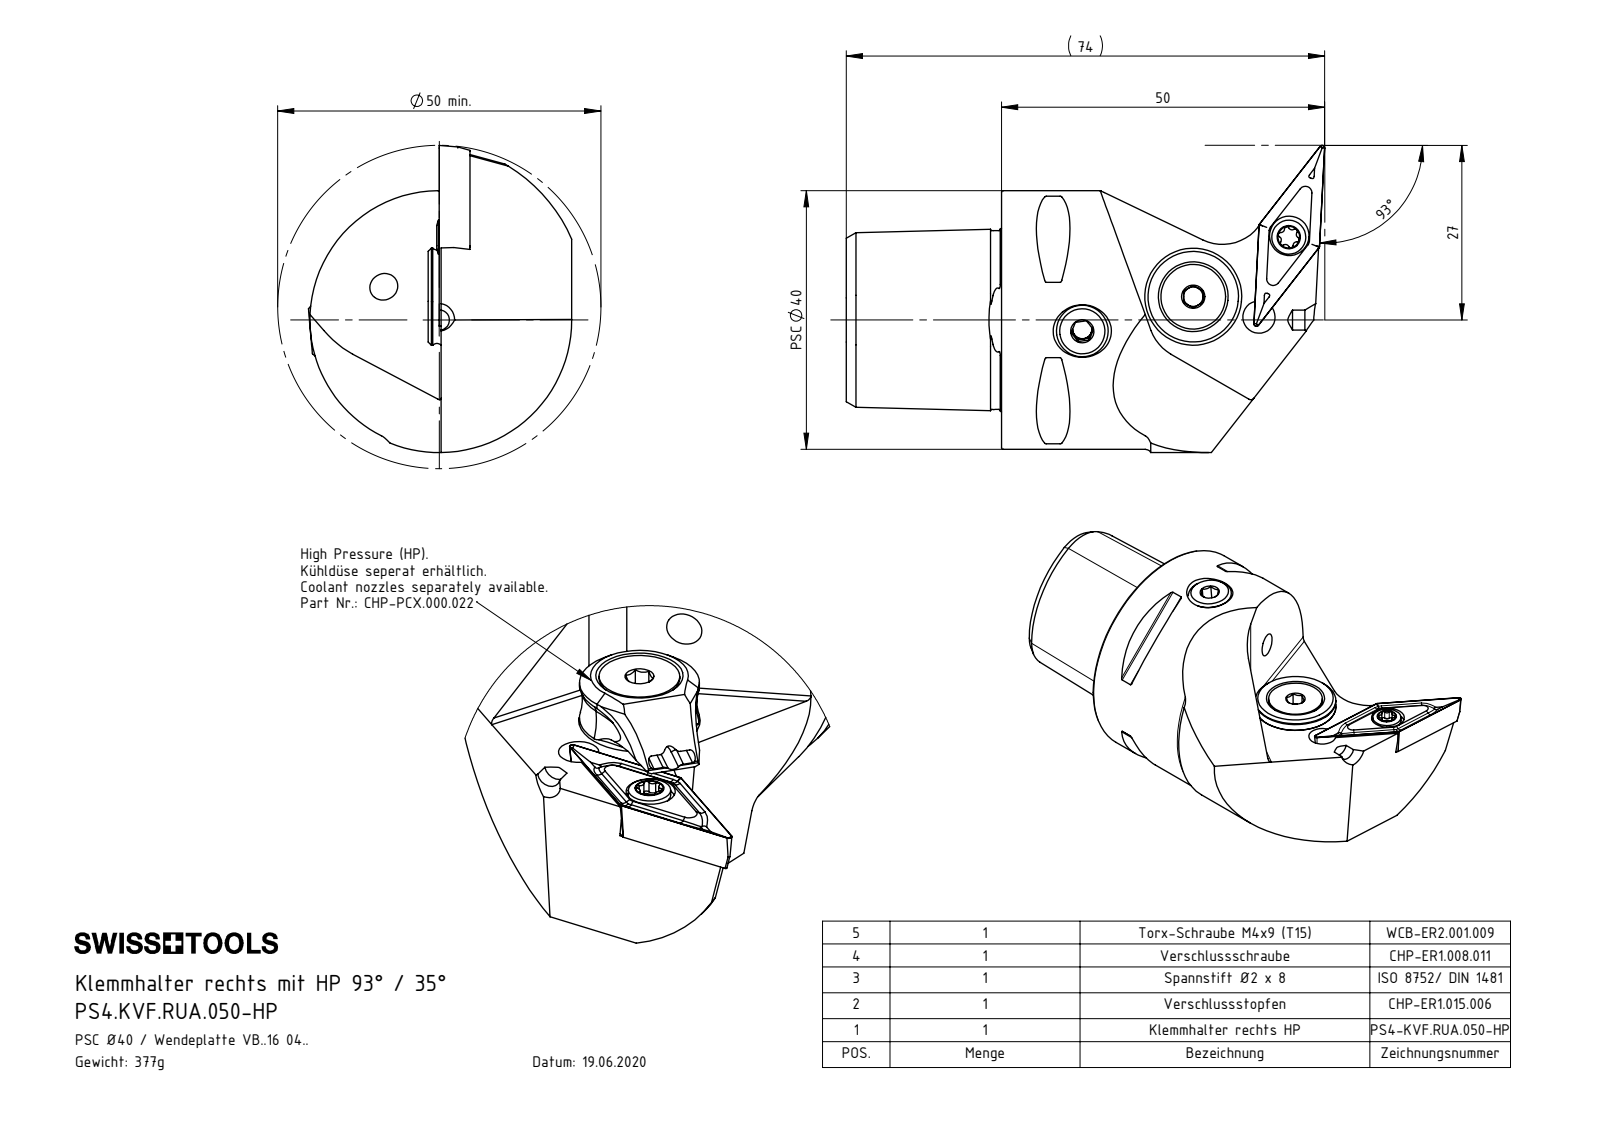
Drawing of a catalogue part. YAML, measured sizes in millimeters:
part_name: "CHP-ER1.008.011_A; PS4.KVF.RUA.050-HP; ISO 8752 2x8; VBMT160404 (+6 more)"
step_written_by: "SolidWorks 2017 (AUTOMOTIVE_DESIGN)"
units: millimeters
bodies: {solids: 8, faces: 284, planar: 92, cylindrical: 66, other: 126}
overall_size: [74, 47.5, 40.73]
volume: 47369
surface_area: 15485
round_holes:
  - {diameter: 3.3, count: 2}
  - {diameter: 4.2, count: 2}
  - {diameter: 5, count: 2}
  - {diameter: 1.2, count: 1}
  - {diameter: 2, count: 1}
  - {diameter: 2.5, count: 1}
  - {diameter: 3, count: 1}
  - {diameter: 4, count: 1}
  - {diameter: 4.4, count: 1}
  - {diameter: 4.6, count: 1}
  - {diameter: 5.2, count: 1}
  - {diameter: 6.1, count: 1}
round_bosses_or_shafts:
  - {diameter: 40, count: 1}
  - {diameter: 15, count: 1}
  - {diameter: 13.4, count: 1}
  - {diameter: 10, count: 1}
  - {diameter: 8, count: 1}
  - {diameter: 5.5, count: 1}
  - {diameter: 5.25, count: 1}
  - {diameter: 5, count: 1}
partial_cylinders:
  - {radius: 0.3, count: 8}
  - {radius: 0.34, count: 6}
  - {radius: 0.59, count: 6}
  - {radius: 0.15, count: 2}
  - {radius: 0.5, count: 2}
  - {radius: 7, count: 2}
  - {radius: 1.57, count: 1}
  - {radius: 3, count: 1}
face_to_face_distances: [20.2, 15.7, 4.5, 15.74, 4.46, 24, 15.52, 35.3, 15, 22.1]
hole_center_spacings: [4.5, 6.74, 10.64, 13.18, 13.4, 13.51, 13.7, 17.41]
